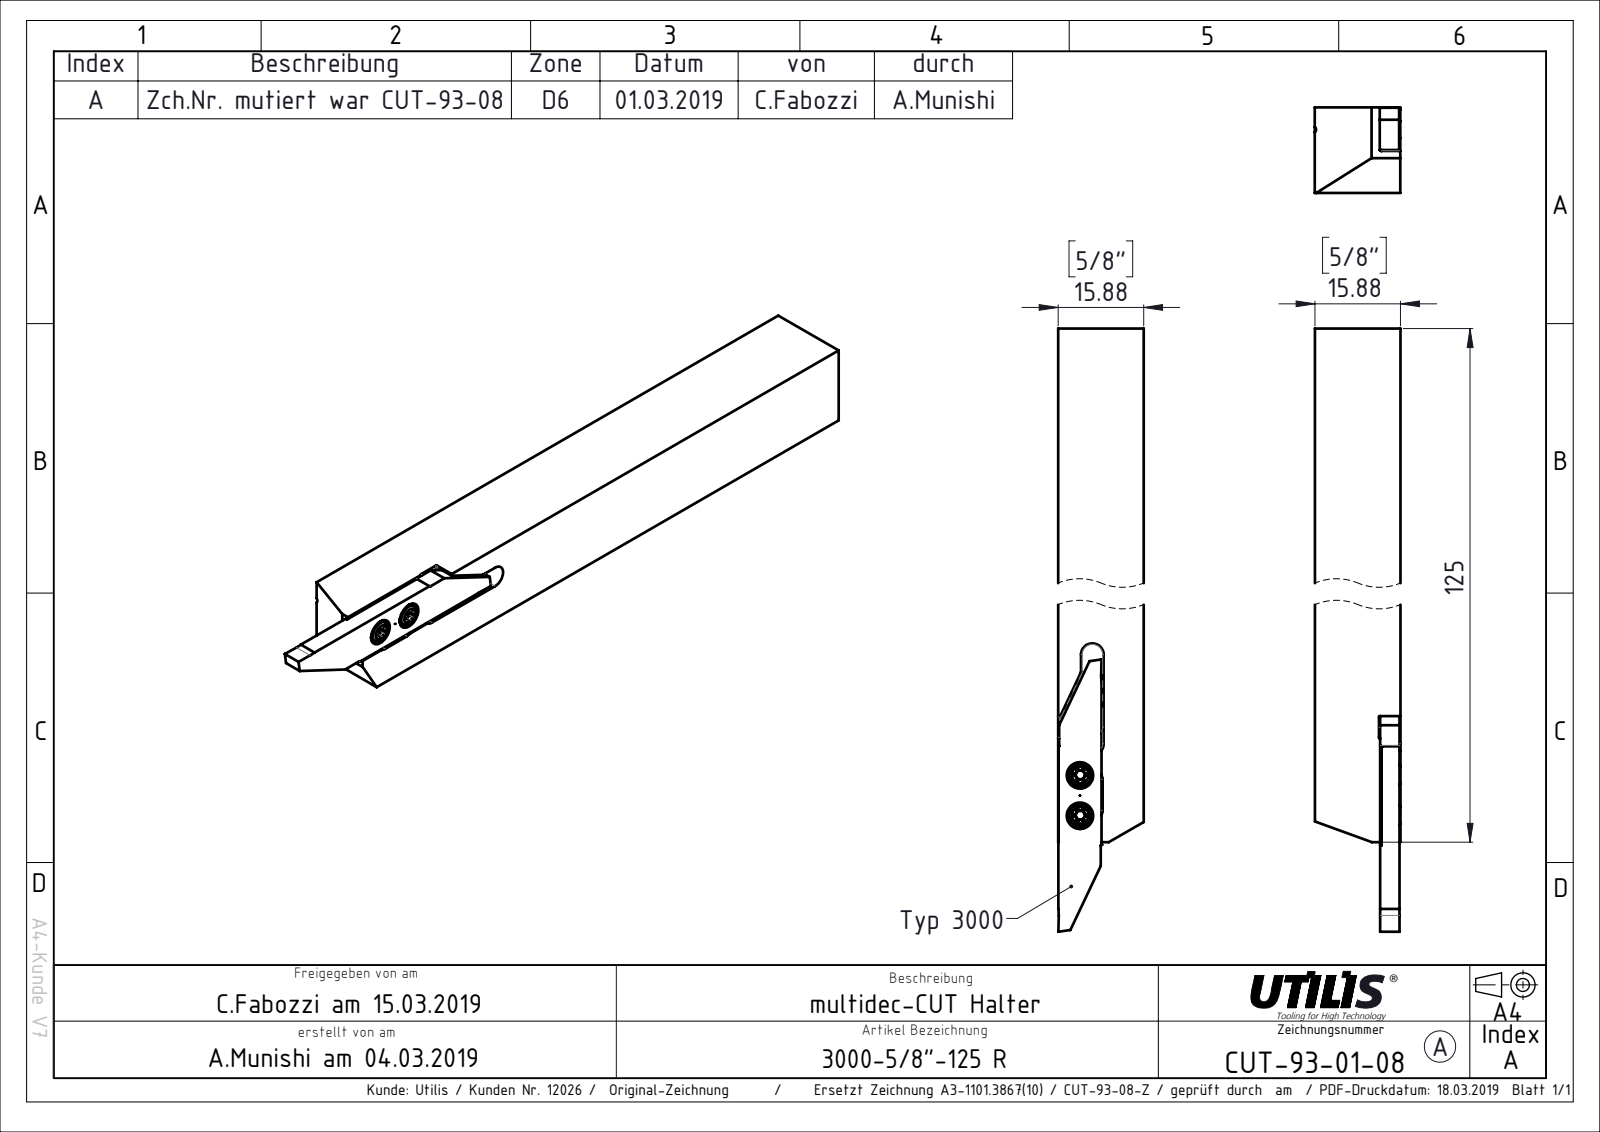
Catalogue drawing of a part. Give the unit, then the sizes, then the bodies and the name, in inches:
Units: inches
Overall size (bounding box): 5.571 × 0.625 × 0.625
Round holes (diameter × count): ⌀0.098 ×2, ⌀0.193 ×2
Partial cylindrical surfaces — rounded edges, fillets, slot ends (radius × count): R0.083 ×4, R0.006 ×2, R0.394 ×2
Main face-to-face distances: 0.625, 0.15, 0.476, 0.142, 0.617, 0.31, 0.315, 0.293, 0.018, 0.333
Hole centre spacings: 0.148, 0.295
Volume: 1.893 in³ · Surface area: 14.94 in²
Bodies: 2 solids, 55 faces (36 planar, 19 cylindrical, 0 other)
Part name (STEP PRODUCT): CUT-Vorlage 3000 R+L Lang Kunde; CUT-93-Kunde; CUT-93-08; CUT-Vorlage 3000 R+L Lang Kunde_R-Lang (+1 more)
STEP written by: SolidWorks 2015 (CONFIG_CONTROL_DESIGN)
